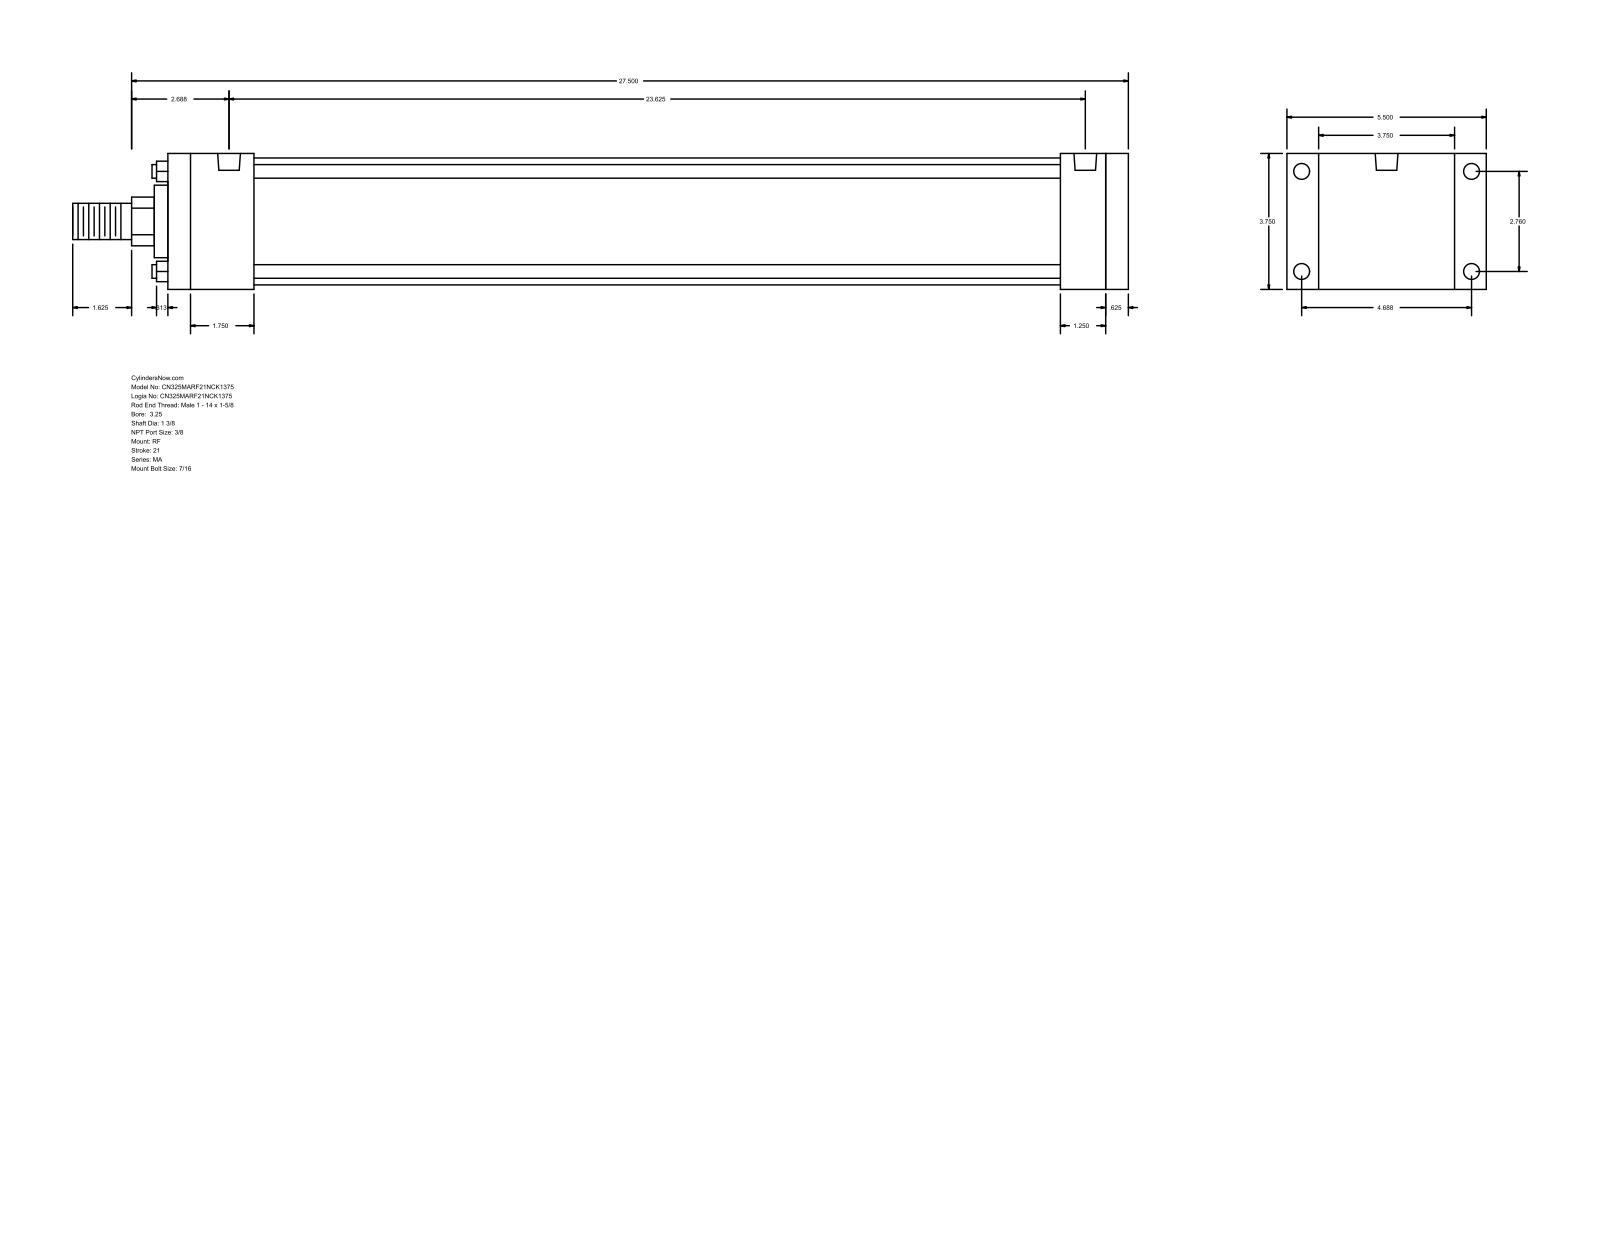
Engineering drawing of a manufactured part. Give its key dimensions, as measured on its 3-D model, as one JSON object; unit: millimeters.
{"part_name": "MA_RF__0325_1.375", "step_written_by": "GSSL Pune (CONFIG_CONTROL_DESIGN)", "units": "millimeters", "bodies": {"solids": 0, "faces": 92, "planar": 64, "cylindrical": 28, "other": 0}, "overall_size": [739.77, 139.7, 95.25], "round_holes": [[11.11, 8], [15.93, 2]], "round_bosses_or_shafts": [[9.53, 4], [88.9, 1], [50.8, 1], [34.92, 1], [25.4, 1]], "partial_cylinders_radius": [[17.06, 1]], "face_to_face_distances": [95.24, 673.1, 15.88, 657.22, 22.23, 117.47, 625.48, 31.74, 47.62, 60.32], "hole_center_spacings": [70.1, 119.06, 138.16, 590.55, 4.76, 4.77, 595.31, 595.32]}
